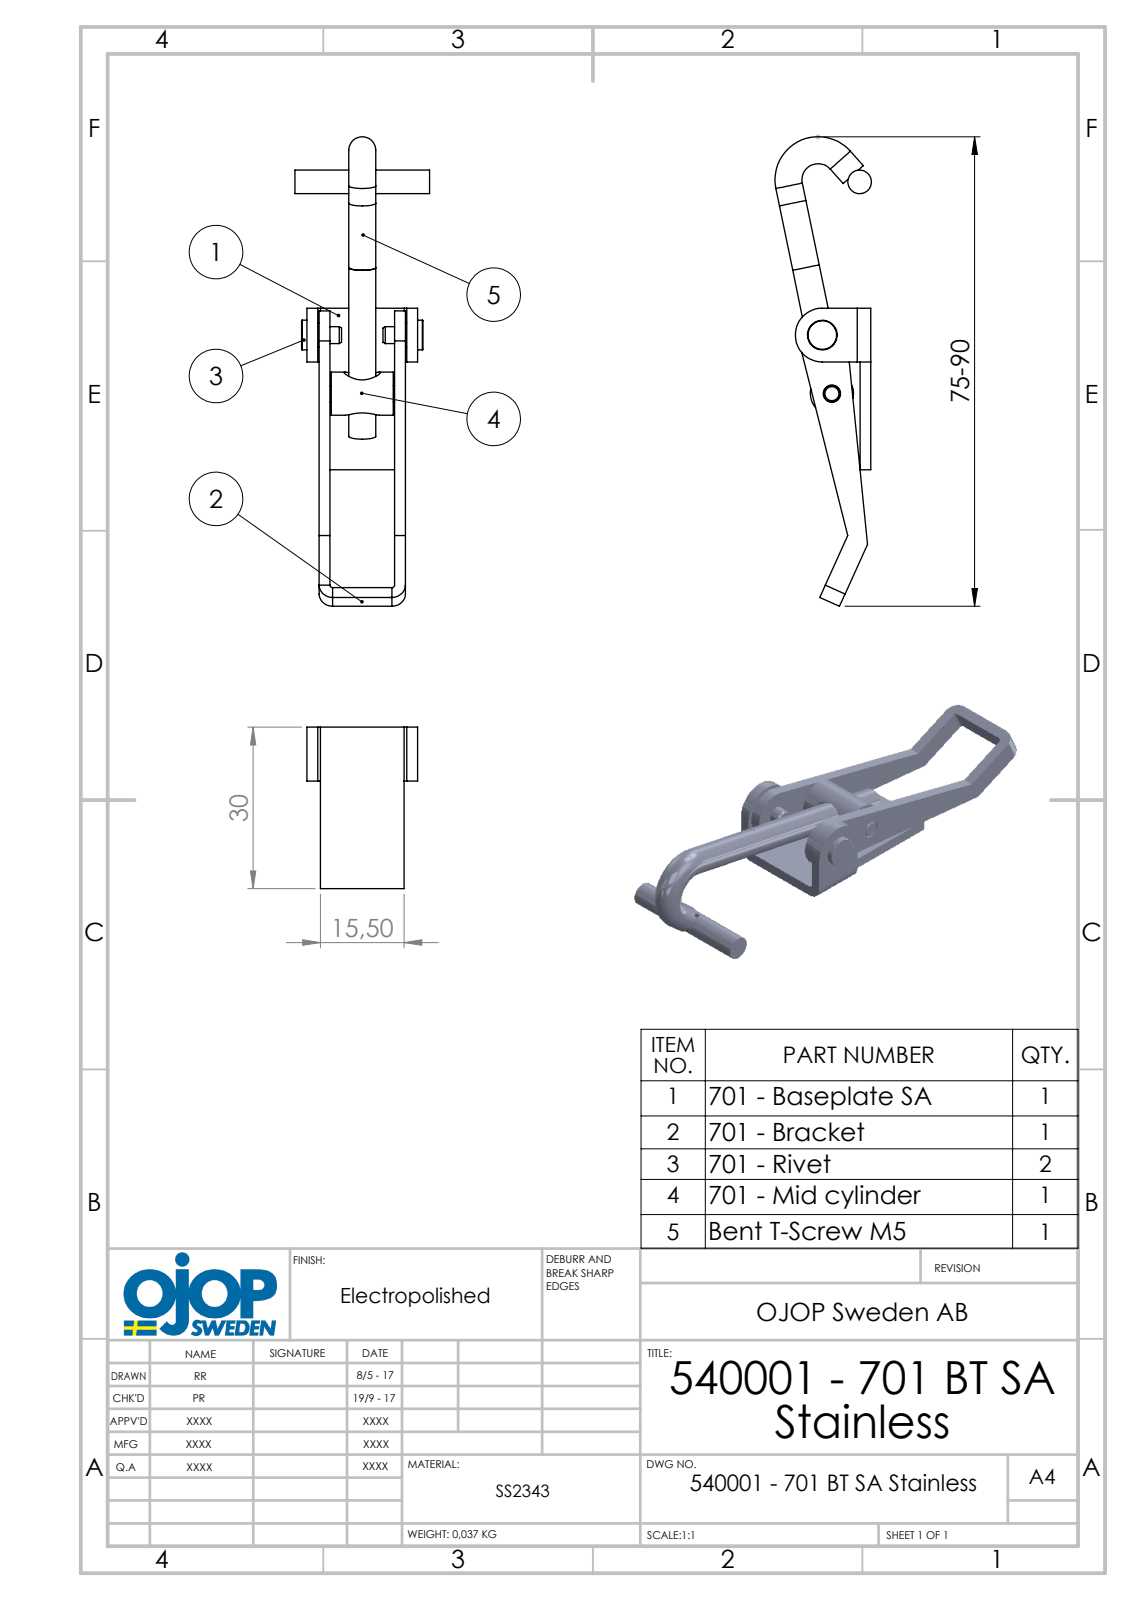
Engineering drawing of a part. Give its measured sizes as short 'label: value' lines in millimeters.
name: Böjd T-skruv M5_Default<As Machined>; 540001 - 701 TSA RF Böjd; 701 - Ansatsnit; 701 - Bygel (+2 more)
written by: SolidWorks 2015 (AUTOMOTIVE_DESIGN)
unit: mm
bodies: 6 solids, 126 faces (53 planar, 55 cylindrical, 18 other)
size: 87.16 × 25 × 17.89
volume: 4 991 mm³; area: 5 779 mm²
holes: 2× ⌀3.2, 1× ⌀4.5, 1× ⌀4.8
bosses: 2× ⌀5, 1× ⌀8, 1× ⌀5.5, 1× ⌀5.01, 1× ⌀4.38, 1× ⌀3.15, 1× ⌀3
rounds: 4× R0.5, 4× R2.5, 1× R4.5, 1× R5
face distances: 2, 14, 2.25, 16, 16.25, 12, 4.25, 18.25, 18.5, 14.25
hole spacings: 11.02
